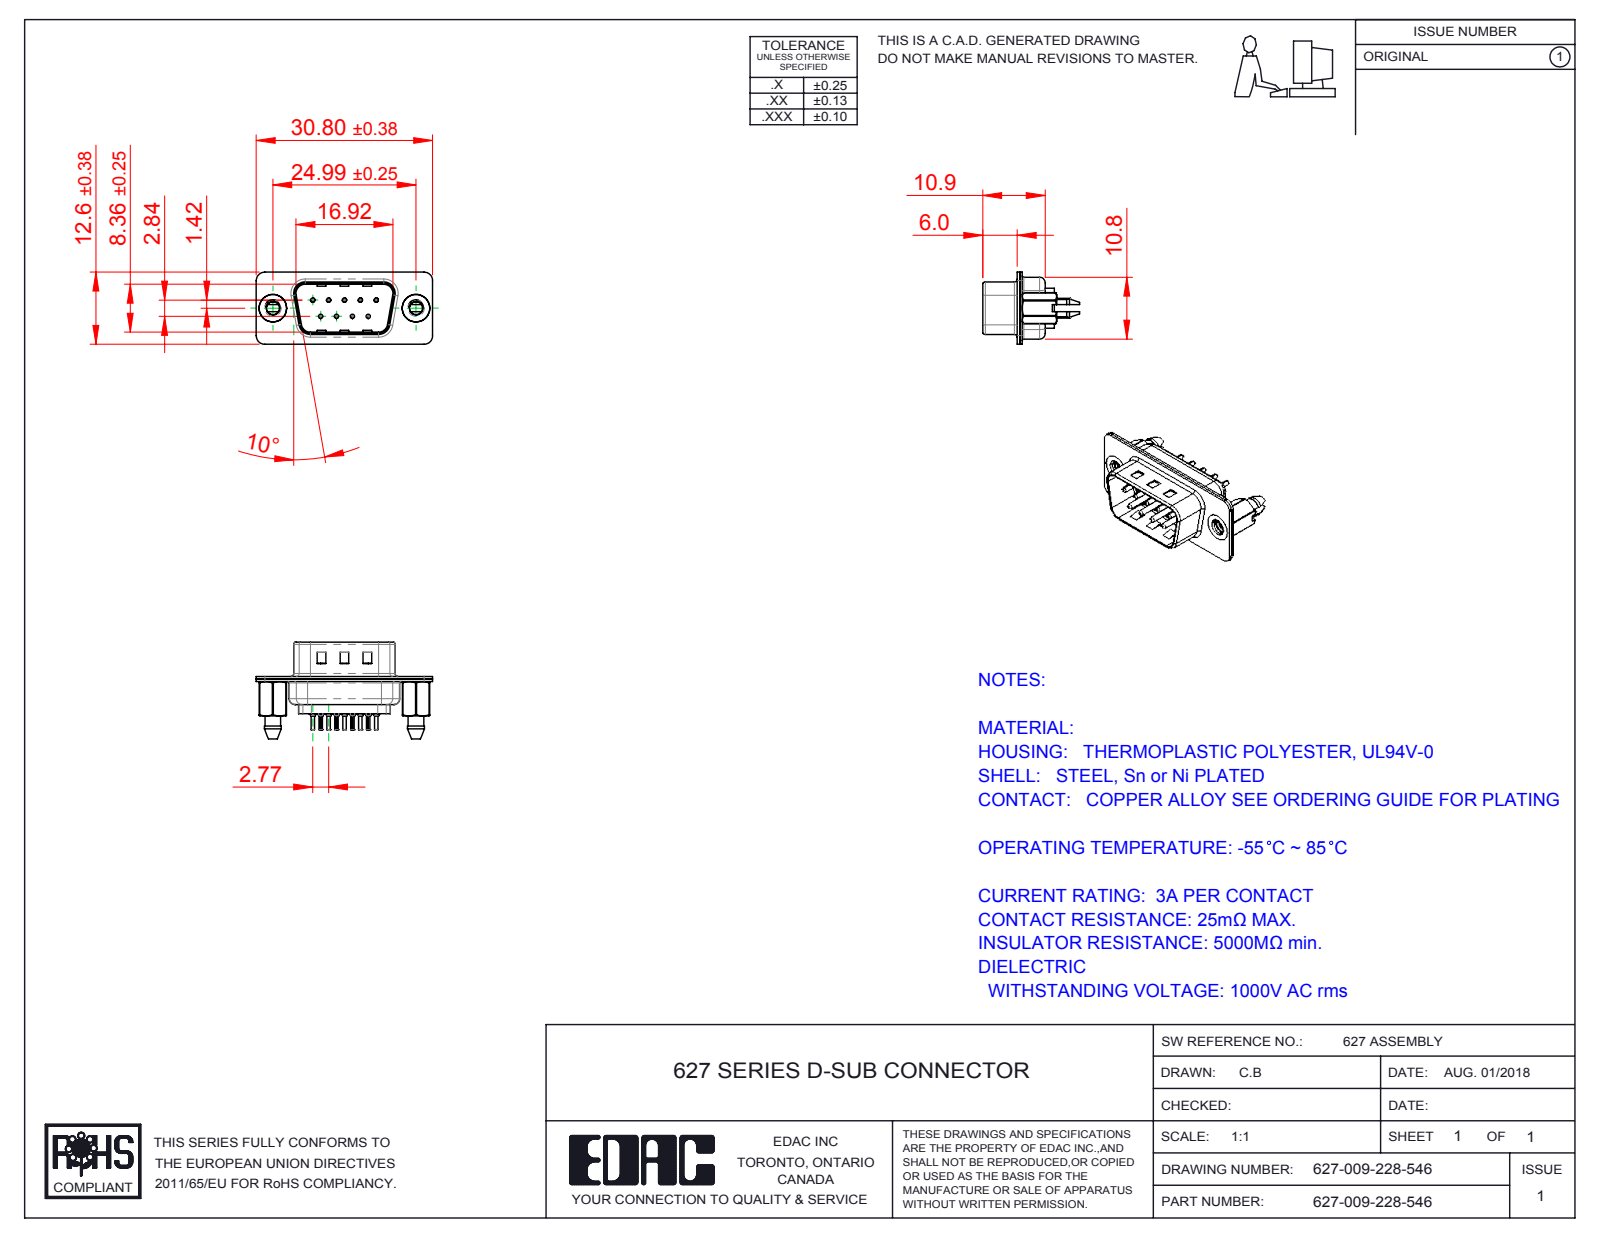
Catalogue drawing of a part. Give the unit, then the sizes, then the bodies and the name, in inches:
Units: inches
Overall size (bounding box): 1.213 × 0.665 × 0.496
Round holes (diameter × count): ⌀0.008 ×9, ⌀0.014 ×9, ⌀0.043 ×9, ⌀0.063 ×9, ⌀0.089 ×2, ⌀0.157 ×2, ⌀0.189 ×2
Round bosses / shafts (diameter × count): ⌀0.079 ×9, ⌀0.059 ×9, ⌀0.03 ×9, ⌀0.024 ×9, ⌀0.193 ×2
Partial cylindrical surfaces — rounded edges, fillets, slot ends (radius × count): R0.059 ×20, R0.004 ×18, R0.079 ×12, R0.063 ×10, R0.02 ×8, R0.01 ×4, R0.024 ×4, R0.026 ×4
Main face-to-face distances: 0.018, 0.016, 0.035, 0.032, 0.377, 0.055, 0.345, 0.256, 0.02, 0.059
Hole centre spacings: 0.124, 0.109, 0.218, 0.198, 0.198, 0.327, 0.294, 0.295
Volume: 0.087 in³ · Surface area: 6.47 in²
Bodies: 14 solids, 1260 faces (355 planar, 494 cylindrical, 411 other)
Part name (STEP PRODUCT): 627 Shell Front_09 Contacts; 627-009-228-546; 627 Contact Row 1_28L; 627 Contact Row 2_28L (+3 more)
STEP written by: SolidWorks 2016 (CONFIG_CONTROL_DESIGN)
